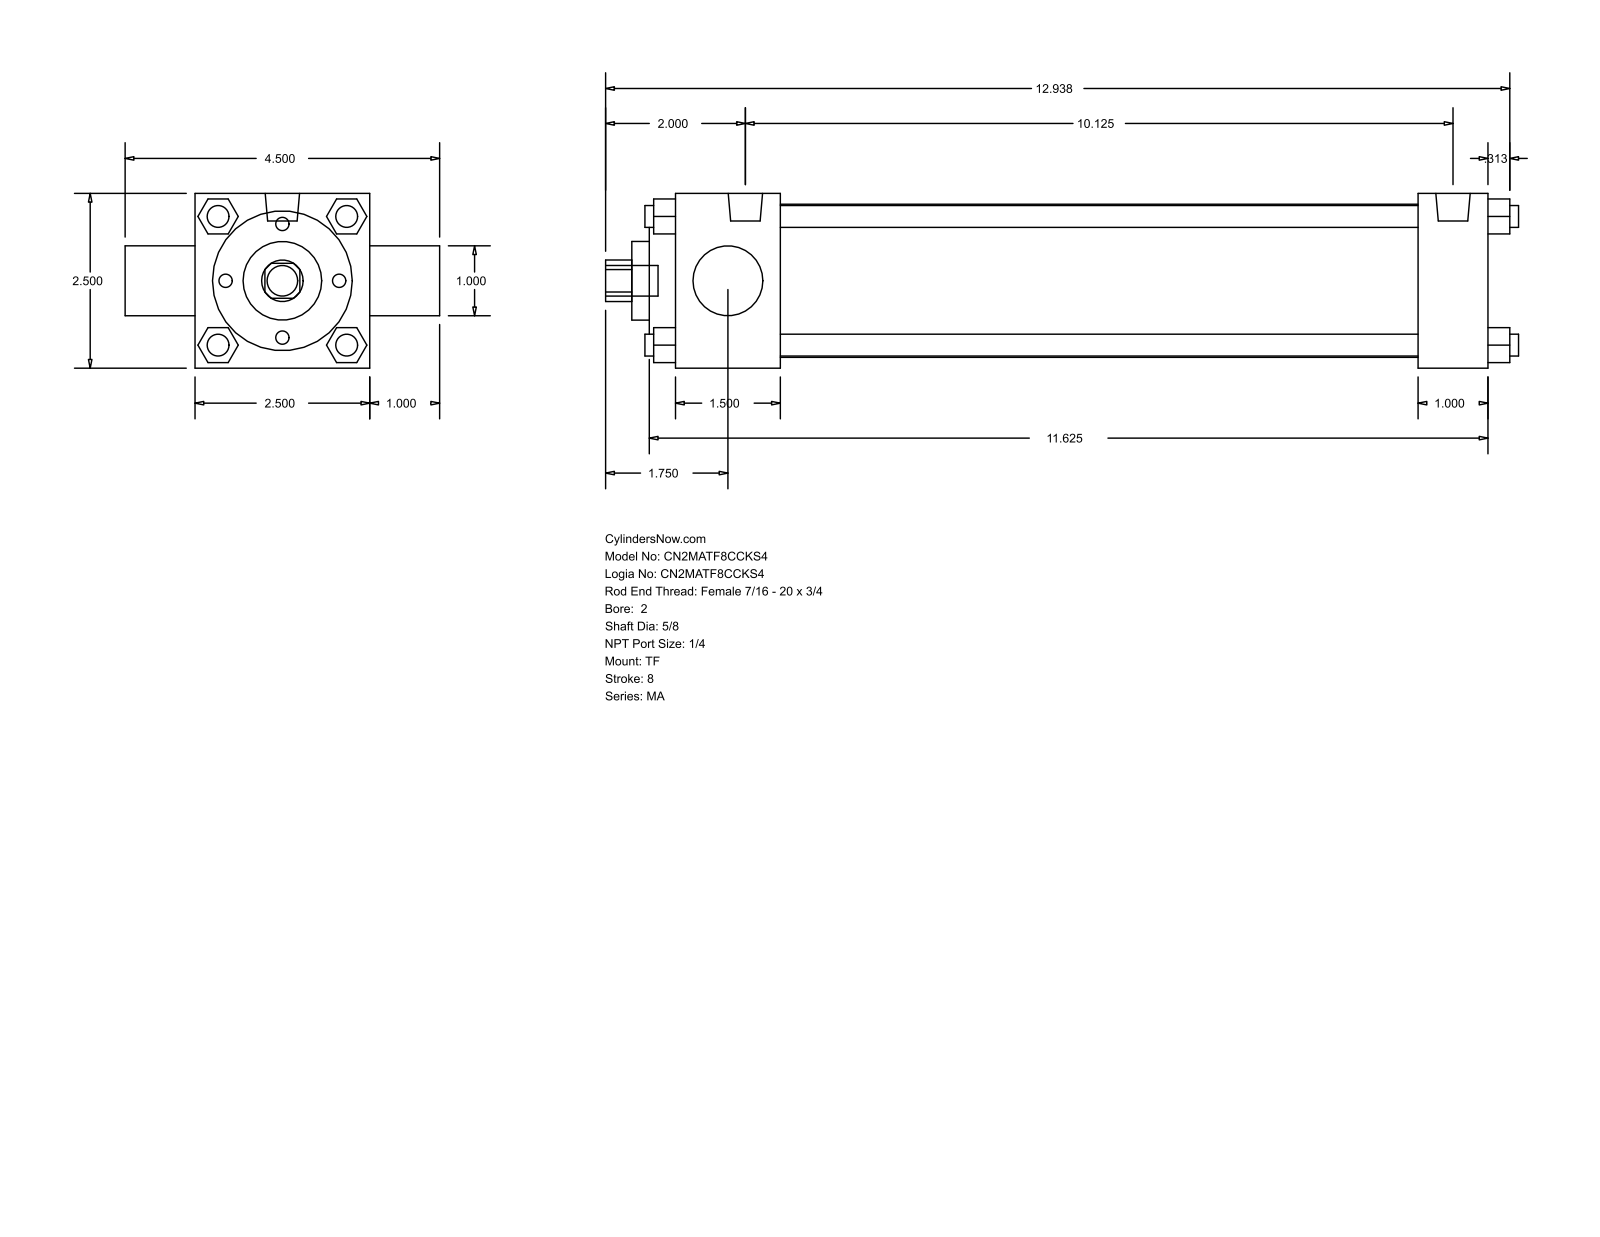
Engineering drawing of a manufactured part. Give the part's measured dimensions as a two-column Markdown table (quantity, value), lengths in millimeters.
| quantity | value |
| --- | --- |
| part name | MA_TF__0200_0.625 |
| STEP written by | GSSL Pune (CONFIG_CONTROL_DESIGN) |
| units | millimeters |
| bodies | 0 solids, 122 faces (93 planar, 29 cylindrical, 0 other) |
| overall size | 331.79 × 114.3 × 63.5 |
| round holes (diameter × count) | 15.88 × 1, 25.4 × 1, 28.57 × 1, 50.8 × 1, 55.63 × 1 |
| round bosses / shafts (diameter × count) | 7.94 × 7, 12.49 × 2, 11.11 × 1 |
| partial cylindrical surfaces (radius × count) | 7.54 × 1 |
| main face-to-face distances | 63.5, 38.1, 12.7, 9.52, 295.28, 269.87, 231.77, 257.18, 25.41, 47.62 |
